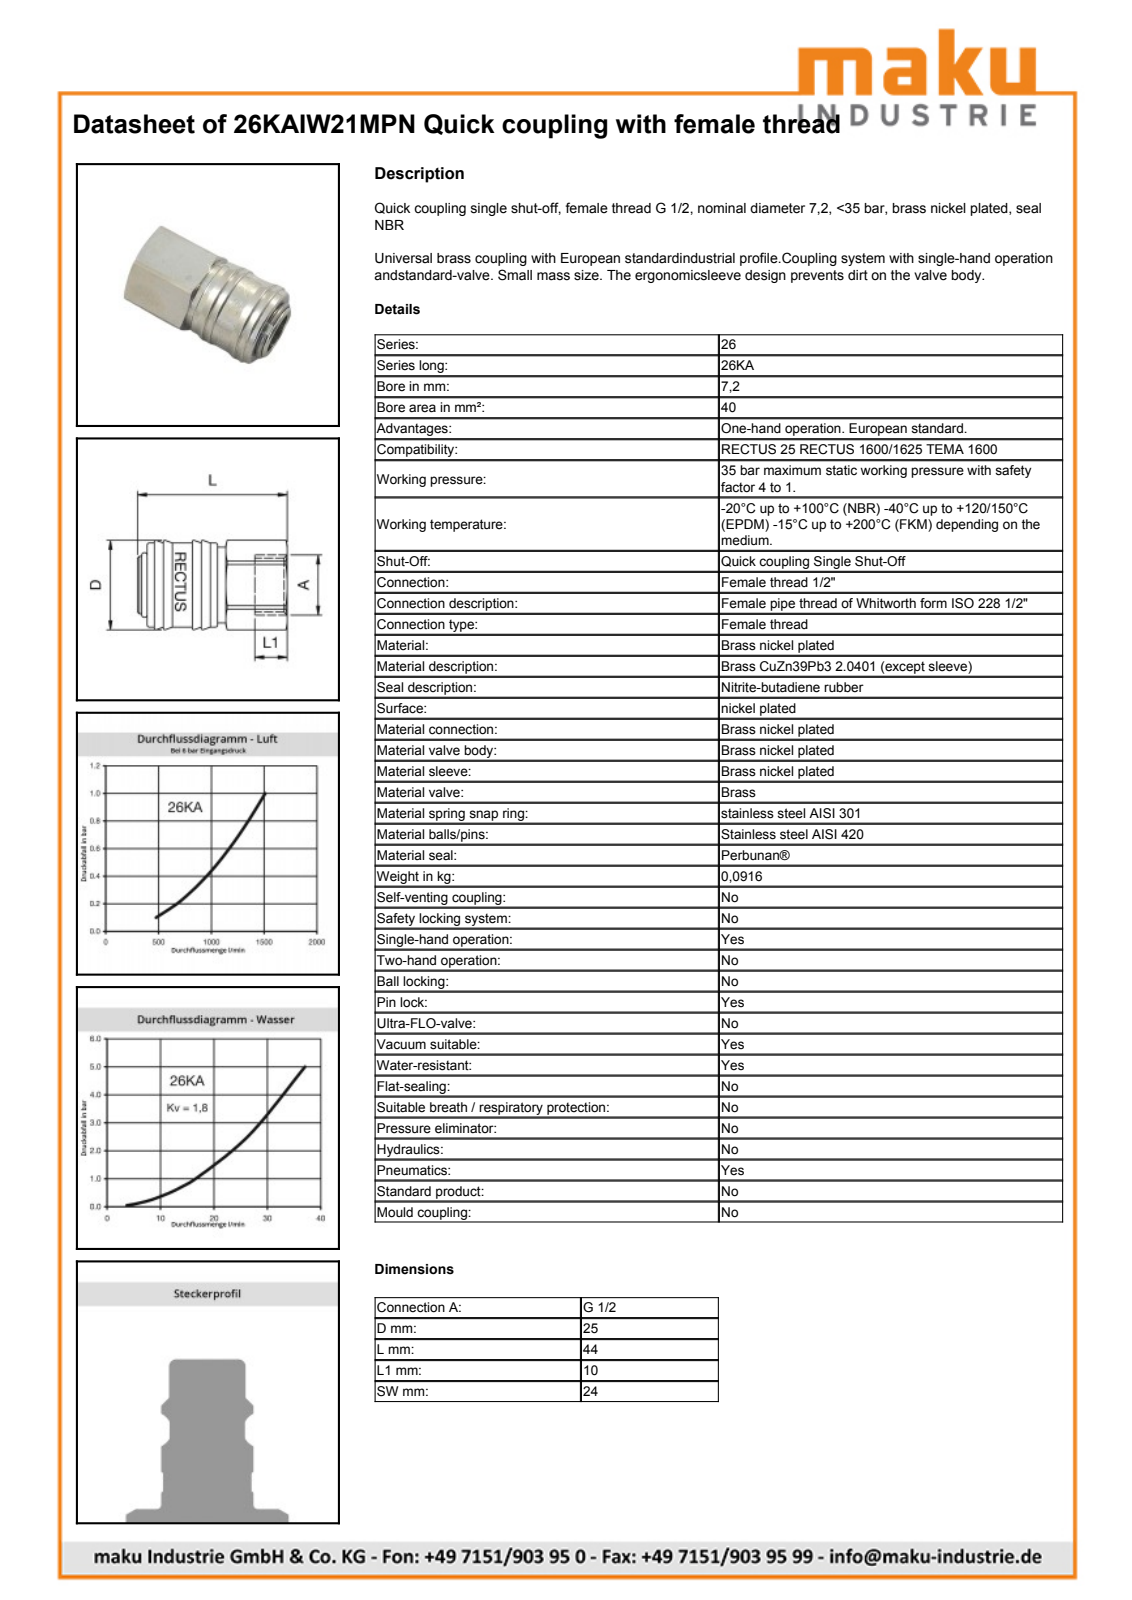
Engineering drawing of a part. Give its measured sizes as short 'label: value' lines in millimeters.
name: D109884
written by: Autodesk Inventor 2013 (AUTOMOTIVE_DESIGN)
unit: mm
bodies: 3 solids, 558 faces (230 planar, 73 cylindrical, 255 other)
size: 44.1 × 26.48 × 26.34
volume: 14 434 mm³; area: 9 659 mm²
holes: 1× ⌀14.45, 1× ⌀14.55, 1× ⌀15.45, 1× ⌀16.1, 1× ⌀17, 1× ⌀18.63, 1× ⌀21.1
bosses: 1× ⌀23.3, 1× ⌀21, 1× ⌀18, 1× ⌀16.65, 1× ⌀15.95, 1× ⌀14.95, 1× ⌀13.99
rounds: 1× R11.55, 1× R13.53
face distances: 24, 29.45, 2.65, 32.1, 21, 8, 44.1, 41.45, 12, 24.1
